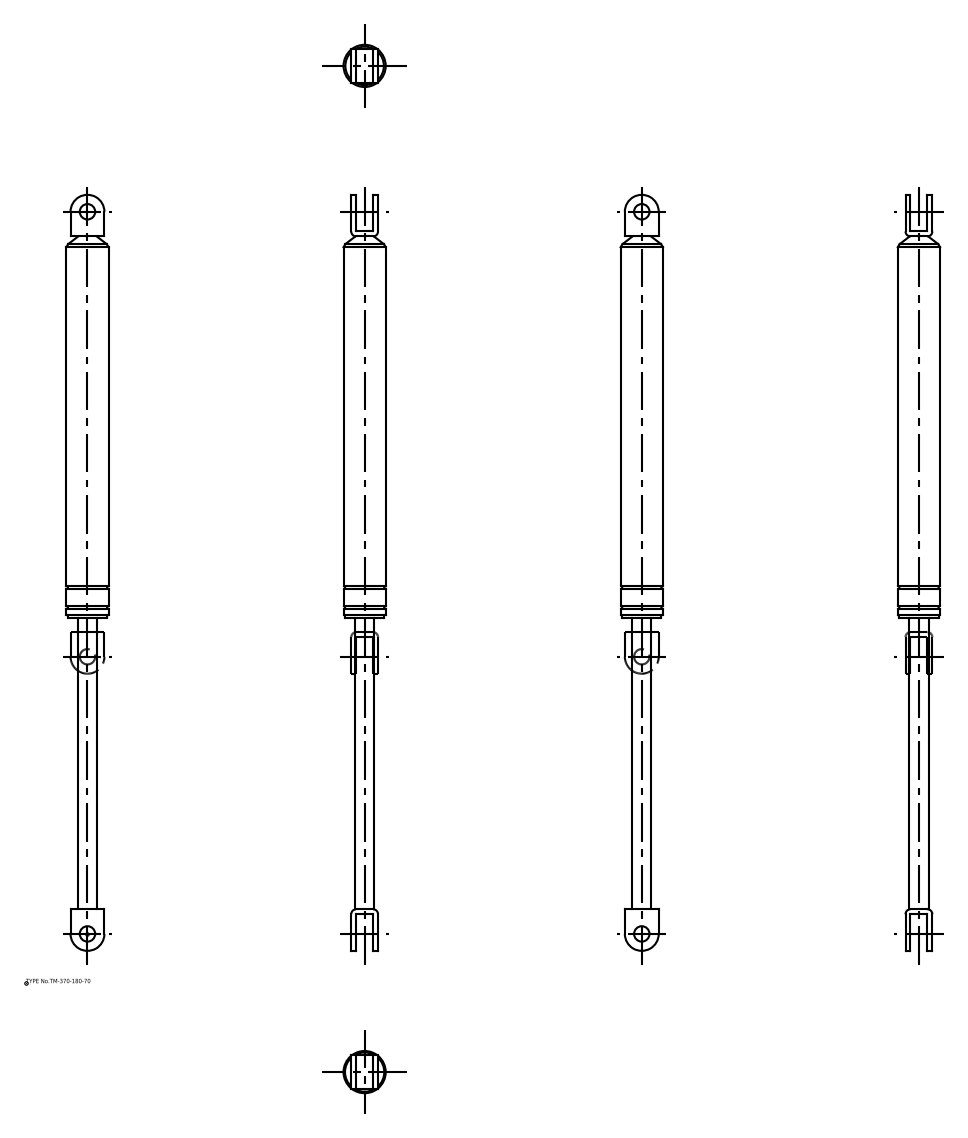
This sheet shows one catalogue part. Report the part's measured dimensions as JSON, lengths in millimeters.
{"part_name": "TM_370_180_70; TM_370_180_70_div", "step_written_by": "spGate 16.7.1 (AUTOMOTIVE_DESIGN)", "units": "millimeters", "bodies": {"solids": 2, "faces": 64, "planar": 22, "cylindrical": 32, "other": 10}, "overall_size": [491, 28.2, 28.2], "volume_mm3": 175124, "surface_area_mm2": 35551, "round_holes": [[10, 2]], "round_bosses_or_shafts": [[28.2, 1], [27.4, 1], [25.5, 1], [12.5, 1]], "partial_cylinders_radius": [[3.2, 4], [11, 2]], "face_to_face_distances": [3.2, 14.2, 17.4, 11, 22, 440.2, 192.2, 443.4, 251.2, 248], "hole_center_spacings": [469]}
